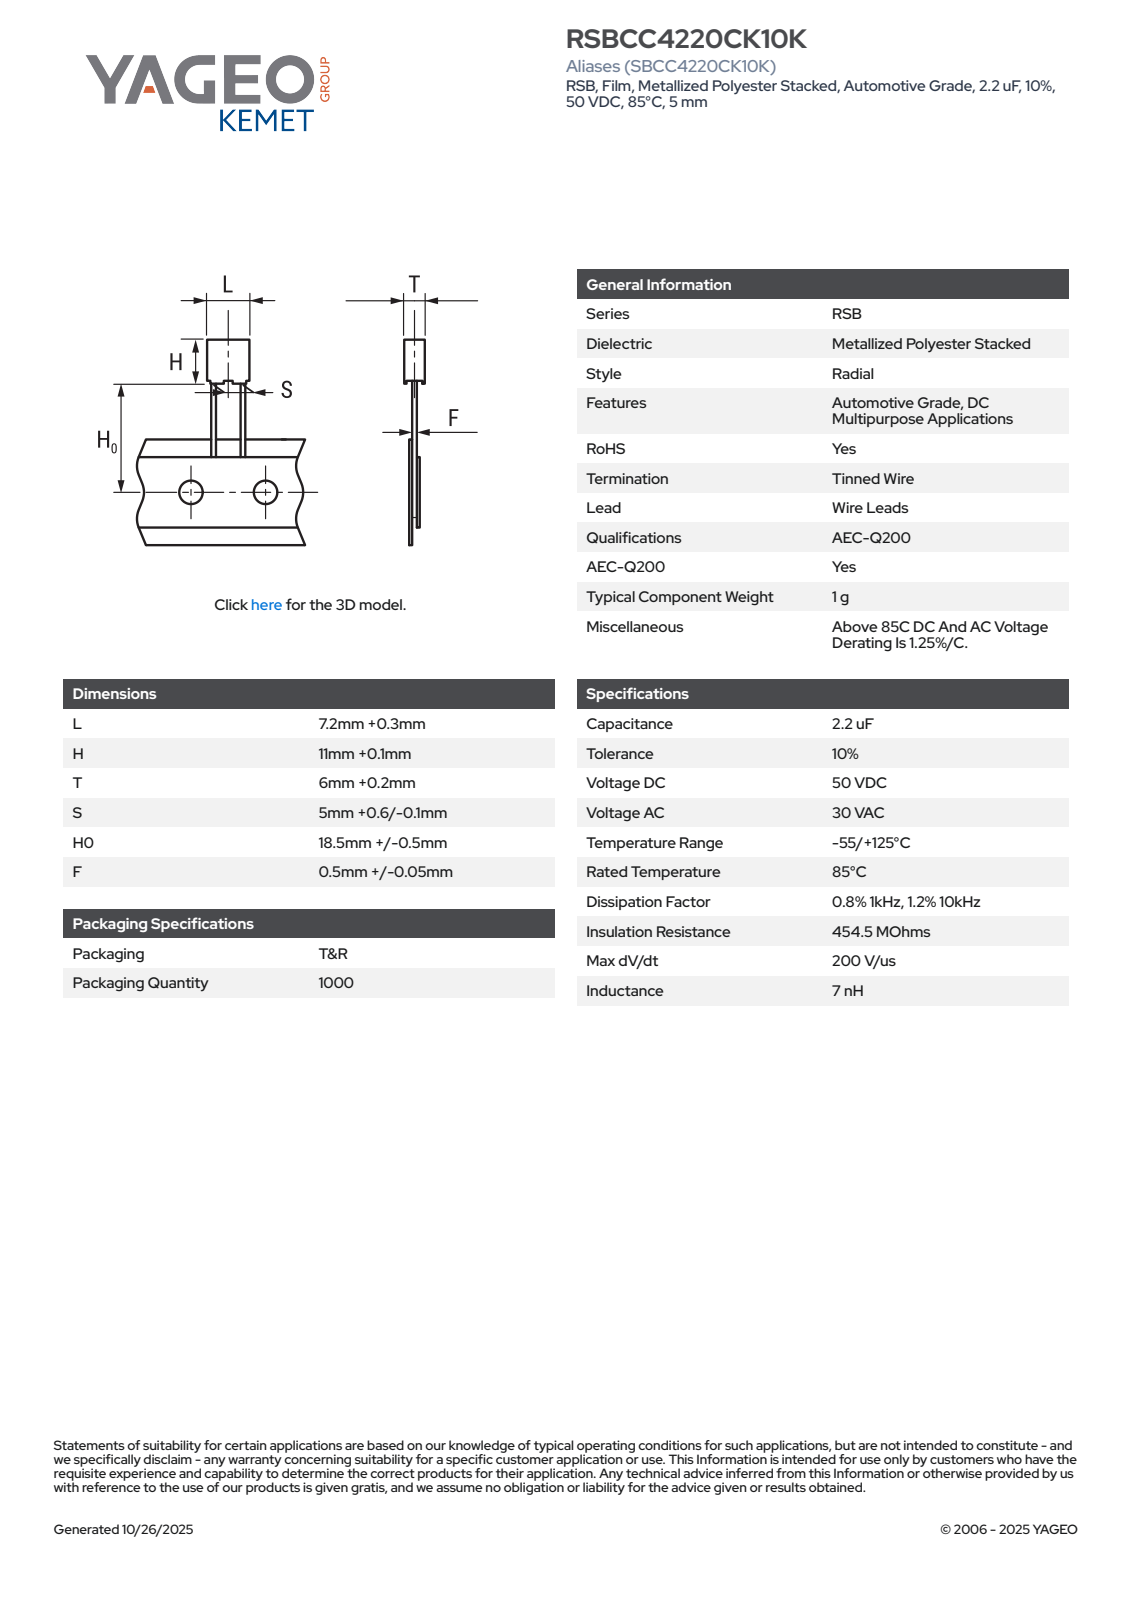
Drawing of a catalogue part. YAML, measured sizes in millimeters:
part_name: "CFR_RB3_7.2X11X6_L7.5H11.1T6.2S5H019F0.65"
step_written_by: "SolidWorks 2014 (AUTOMOTIVE_DESIGN)"
units: millimeters
bodies: {solids: 4, faces: 85, planar: 77, cylindrical: 8, other: 0}
overall_size: [30.1, 7.5, 6.21]
volume: 498
surface_area: 493
round_bosses_or_shafts:
  - {diameter: 0.65, count: 2}
partial_cylinders:
  - {radius: 0.5, count: 4}
face_to_face_distances: [6.2, 7.5, 10.35, 5.95, 7.25, 0.75, 11.1, 5.7, 7, 0.38]
